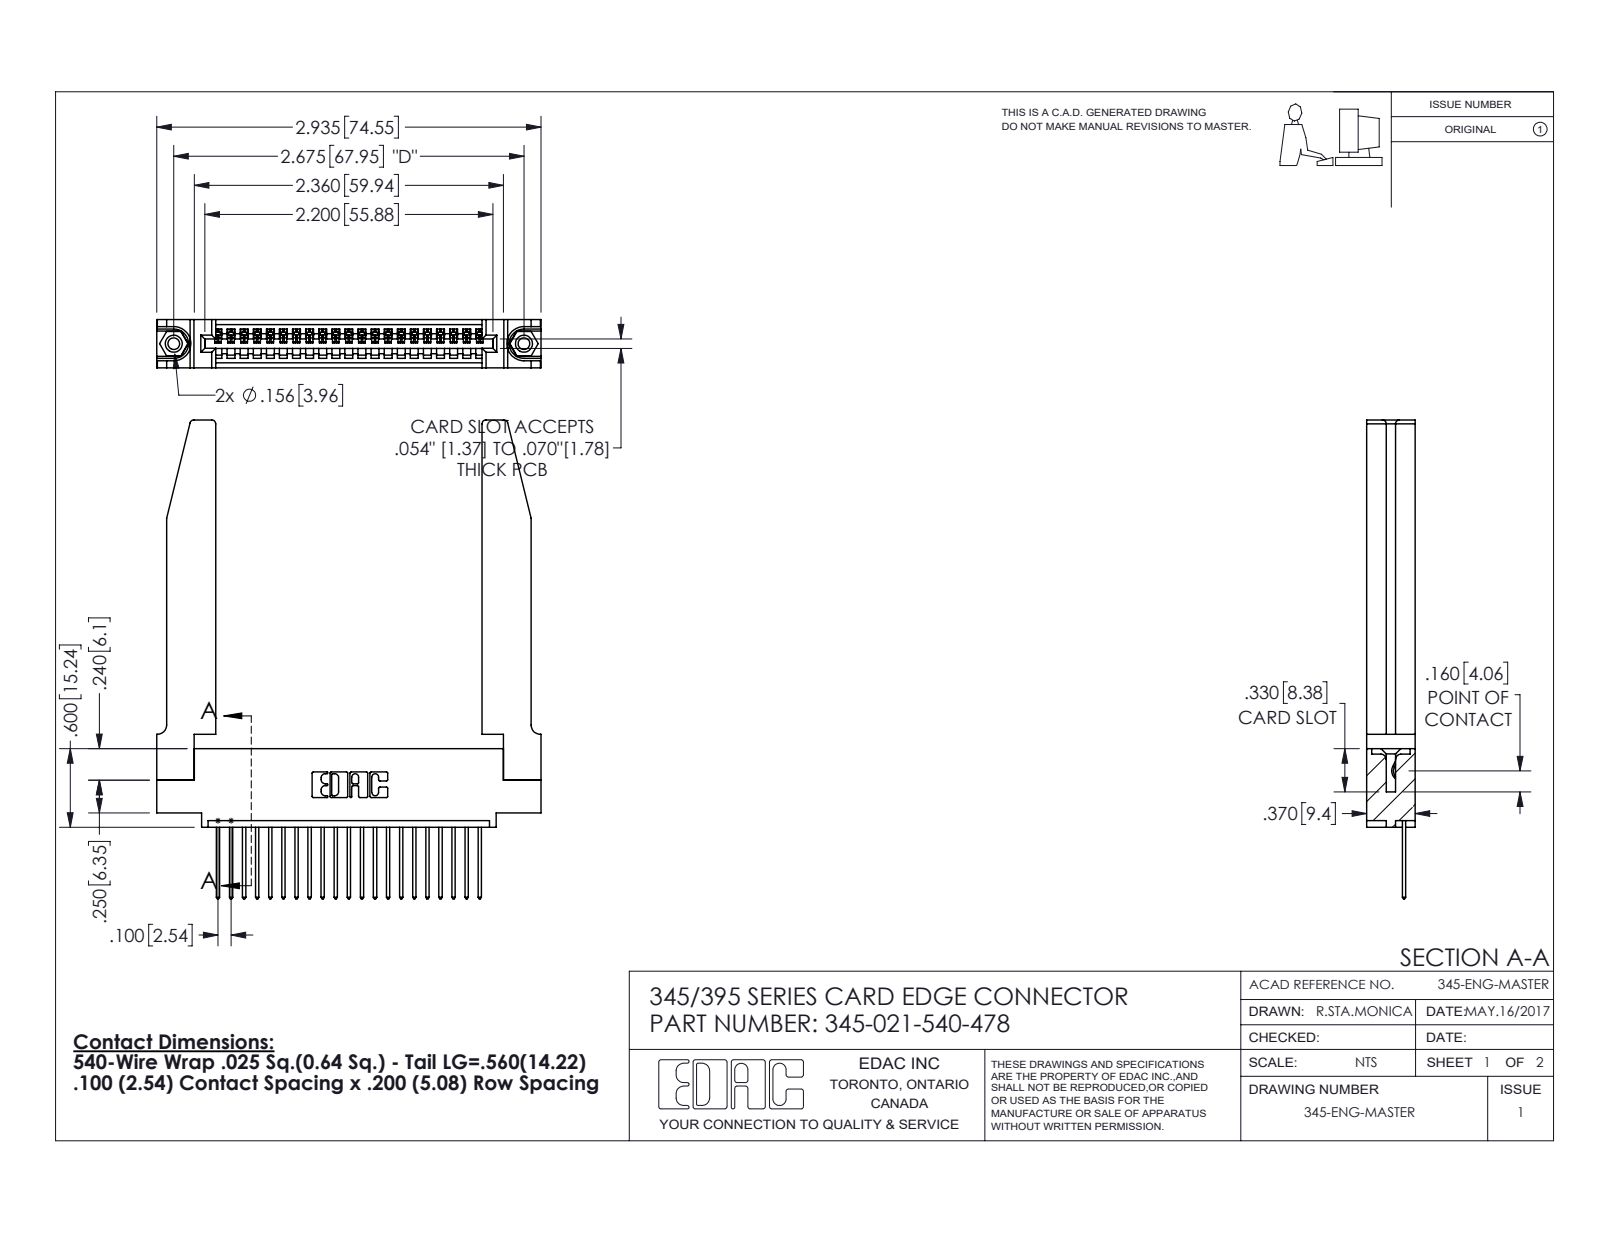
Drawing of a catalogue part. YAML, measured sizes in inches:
part_name: "345 Part_0.110 Offset - 0.156 Dia-TH; 345-220-078_345-220-078; 345-250-001_345-250-001-102; 345-292-001_345-293-140 (+1 more)"
step_written_by: "SolidWorks 2016 (CONFIG_CONTROL_DESIGN)"
units: inches
bodies: {solids: 26, faces: 1582, planar: 1066, cylindrical: 464, other: 52}
overall_size: [3.657, 2.936, 0.37]
volume: 0.893
surface_area: 24.76
round_holes:
  - {diameter: 0.089, count: 2}
  - {diameter: 0.125, count: 2}
  - {diameter: 0.156, count: 2}
  - {diameter: 0.064, count: 1}
round_bosses_or_shafts:
  - {diameter: 0.155, count: 2}
partial_cylinders:
  - {radius: 0.006, count: 42}
  - {radius: 0.01, count: 42}
  - {radius: 0.01, count: 22}
  - {radius: 0.03, count: 8}
  - {radius: 0.007, count: 6}
  - {radius: 0.031, count: 6}
  - {radius: 0.026, count: 3}
  - {radius: 0.031, count: 2}
face_to_face_distances: [0.37, 0.072, 0.298, 0.098, 0.272, 0.025, 0.2, 0.15, 0.148, 0.22]
hole_center_spacings: [0.27, 2.441, 2.675]
